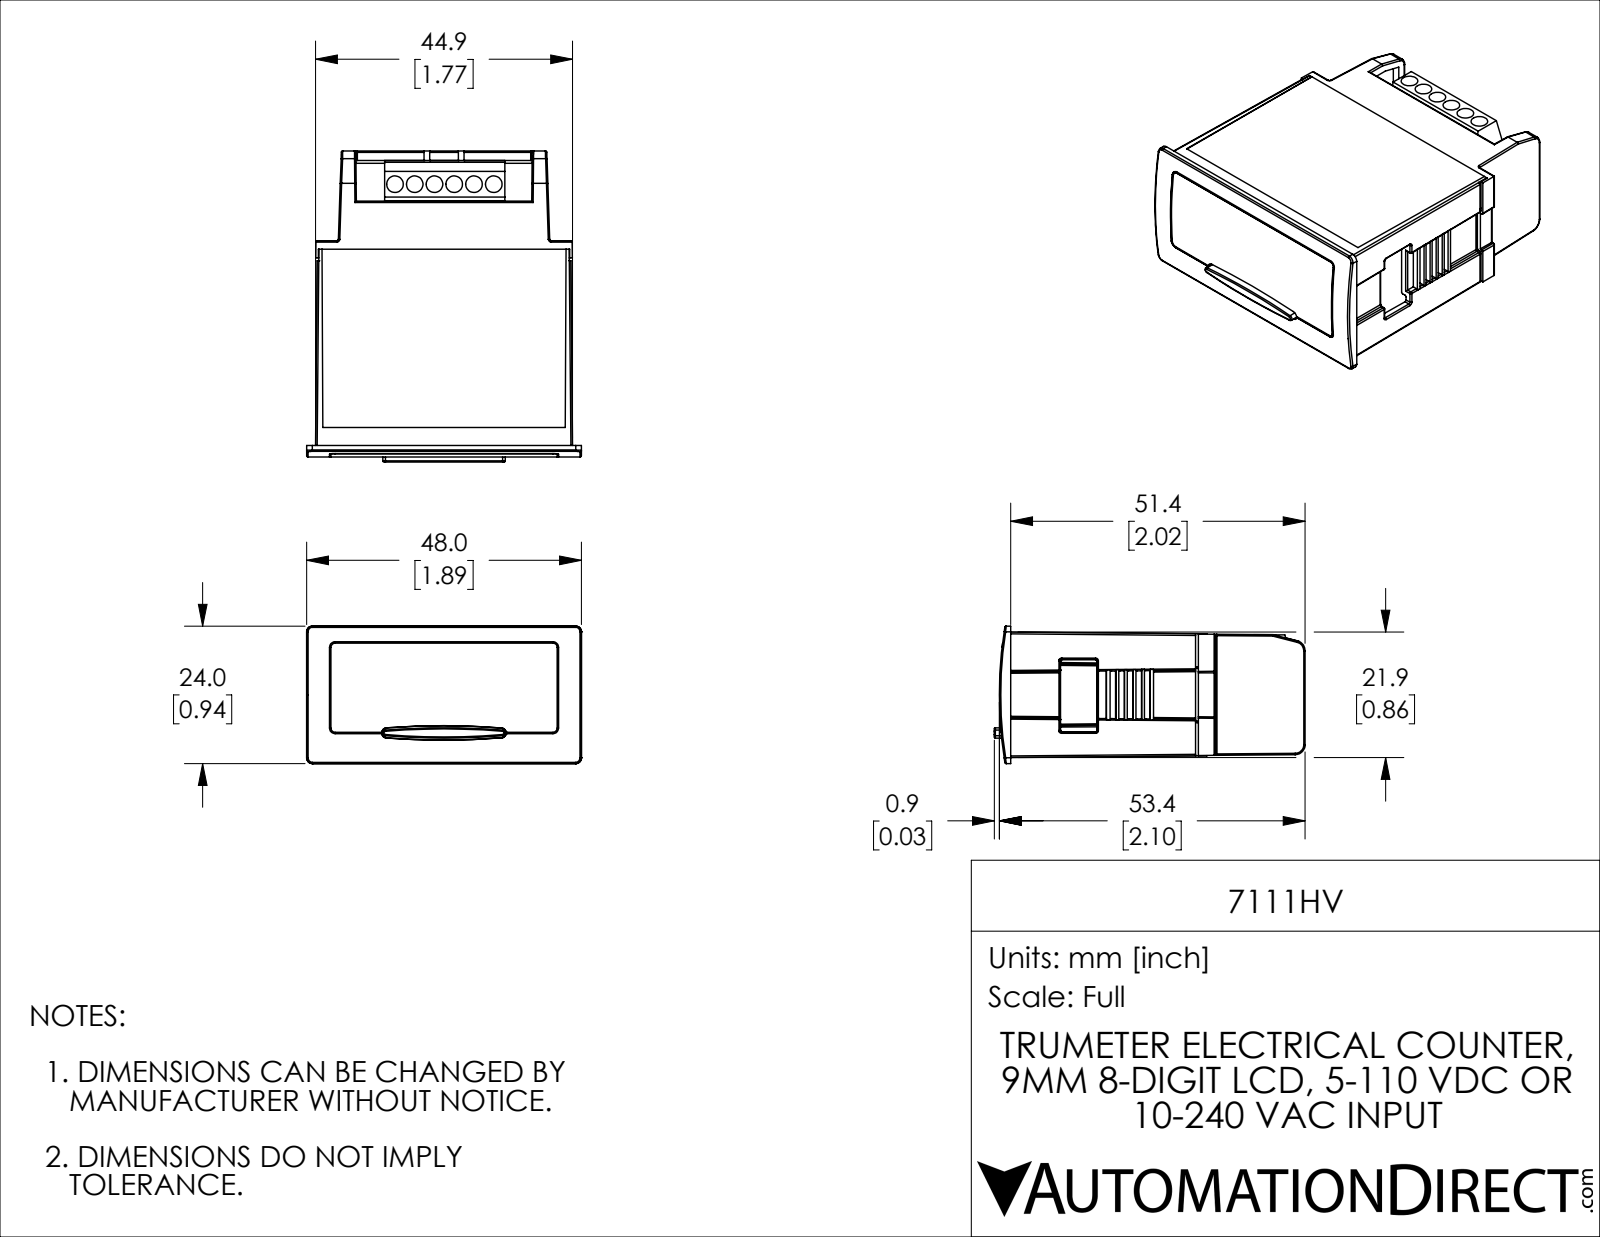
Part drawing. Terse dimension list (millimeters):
name: 7111HV
written by: SolidWorks 2021 (CONFIG_CONTROL_DESIGN)
unit: mm
bodies: 2 solids, 1771 faces (1106 planar, 291 cylindrical, 374 other)
size: 54.3 × 48 × 24
volume: 15 500 mm³; area: 21 700 mm²
holes: 6× ⌀2.9
bosses: 3× ⌀3.8, 1× ⌀1.8
rounds: 157× R0.3, 12× R1, 11× R0.5, 4× R0.3, 4× R0.8, 2× R0.5, 2× R1.8, 2× R128.7
face distances: 20.4, 1.7, 1.8, 42.4, 18.7, 20.4, 1.3, 1.5, 1.1, 43.5
hole spacings: 3.5, 6.9, 10.3, 13.8, 17.2
